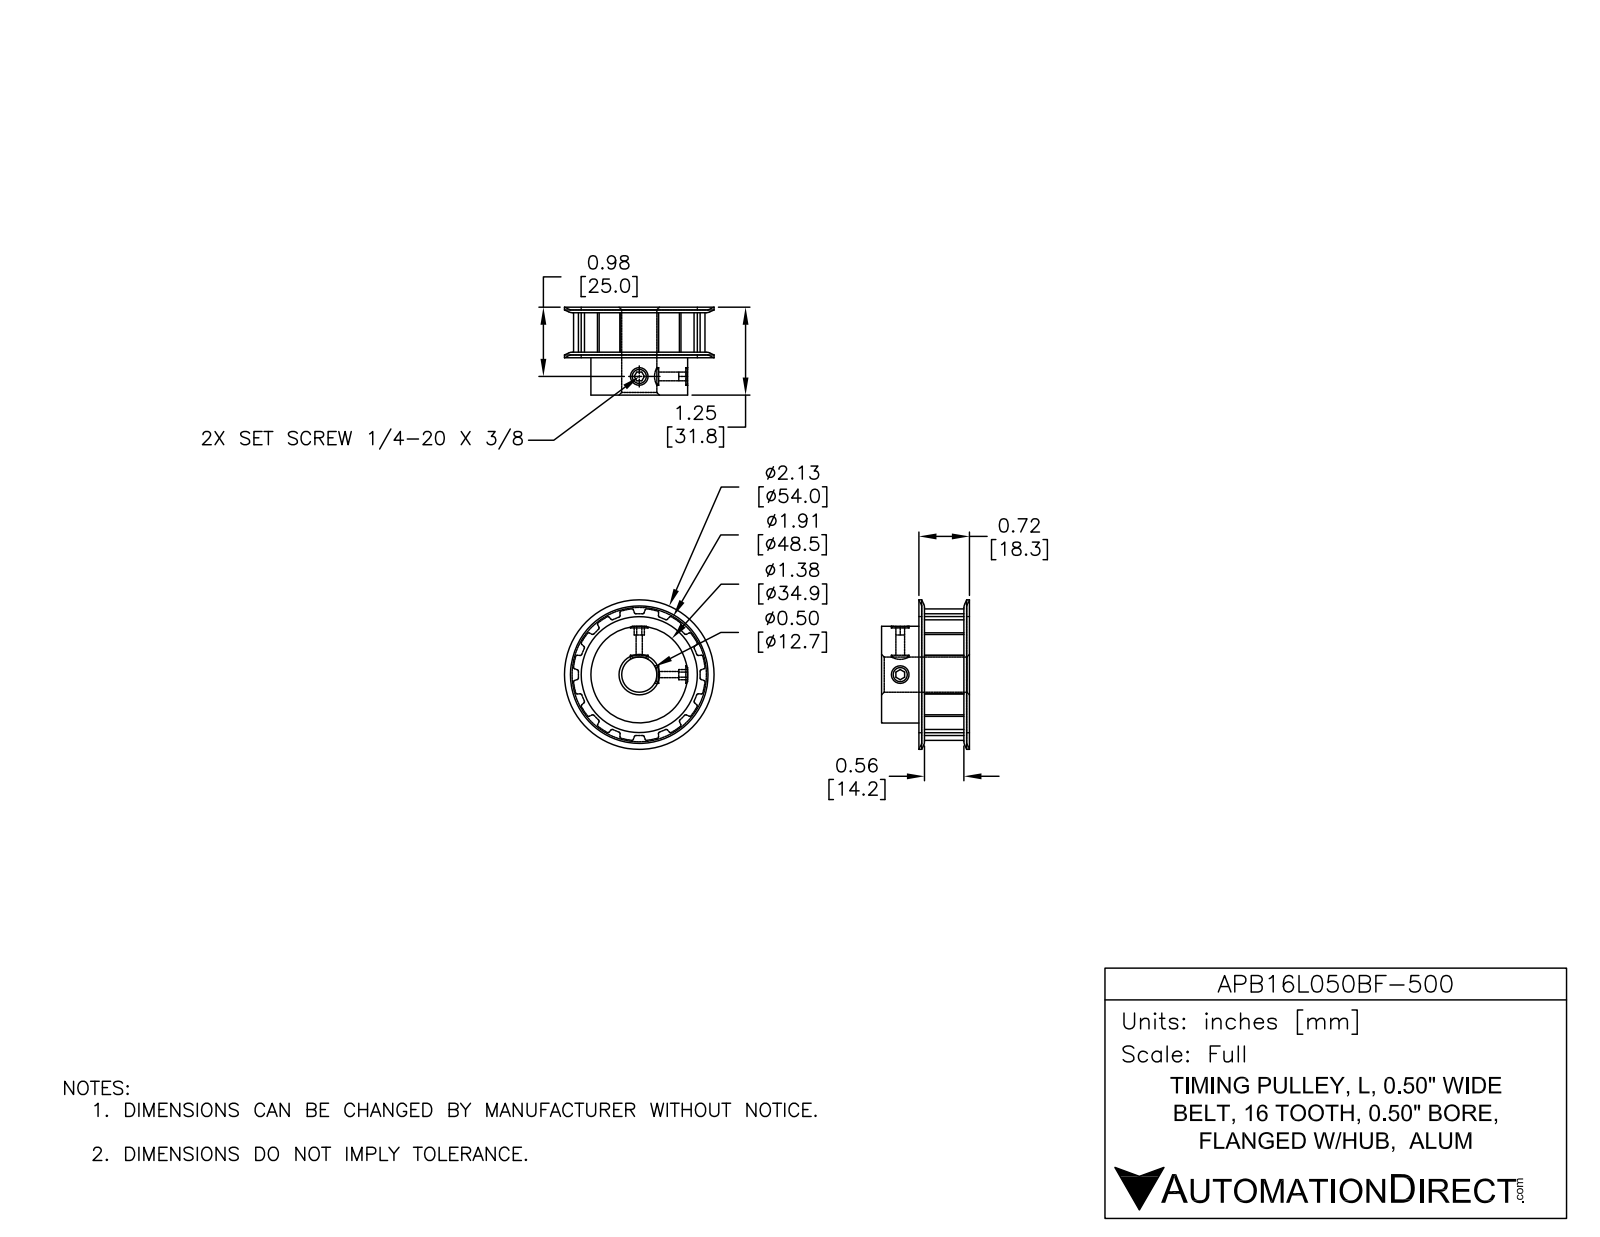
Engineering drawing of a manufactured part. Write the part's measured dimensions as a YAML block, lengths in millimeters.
part_name: "APB16L050BF-500"
step_written_by: "SolidWorks 2014 (AUTOMOTIVE_DESIGN)"
units: millimeters
bodies: {solids: 1, faces: 140, planar: 54, cylindrical: 64, other: 22}
overall_size: [54, 54, 31.8]
volume: 40360
surface_area: 11320
round_holes:
  - {diameter: 2.2, count: 2}
  - {diameter: 12.7, count: 1}
round_bosses_or_shafts:
  - {diameter: 34.9, count: 1}
partial_cylinders:
  - {radius: 0.4, count: 32}
  - {radius: 22.5, count: 1}
face_to_face_distances: [16.3, 1, 17.3, 31.8, 30.7, 14.5, 47.8, 17.9, 47.8, 1]
